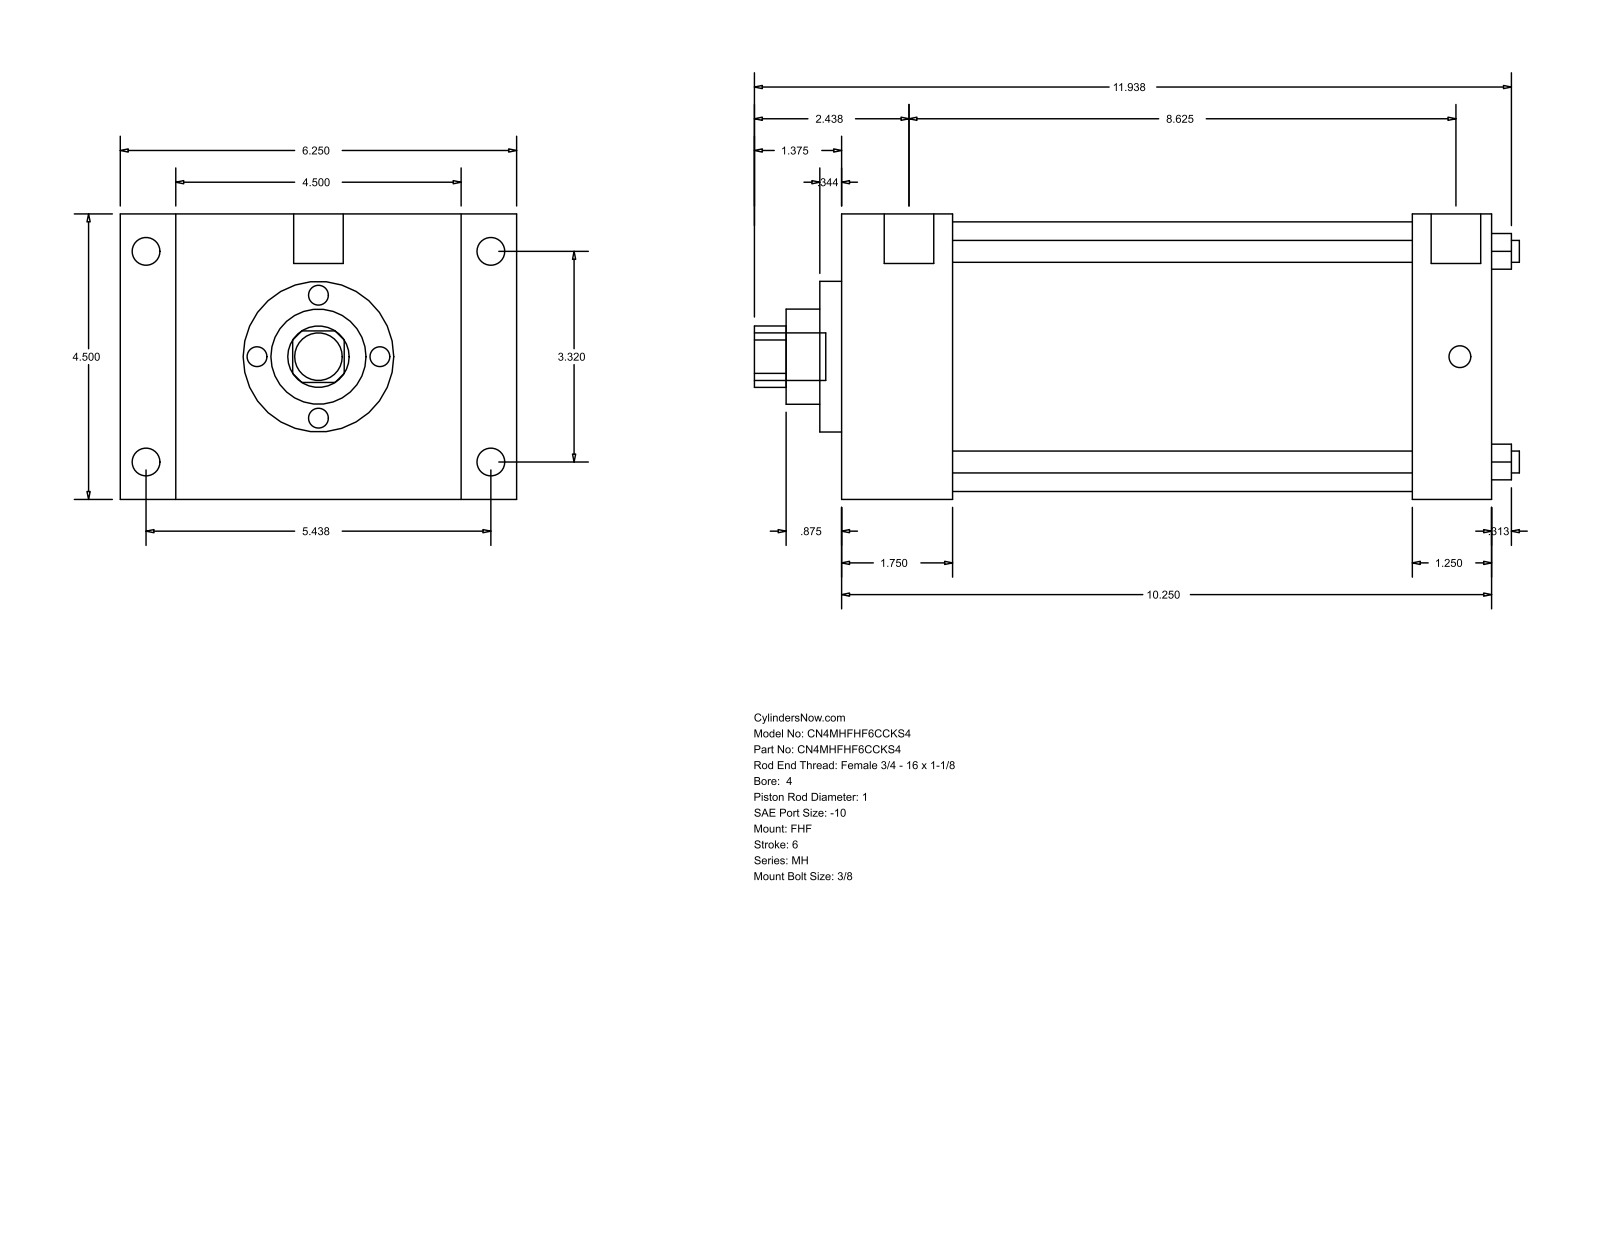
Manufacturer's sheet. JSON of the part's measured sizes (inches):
{"part_name": "MH_FHF__0400_1", "step_written_by": "GSSL Pune (CONFIG_CONTROL_DESIGN)", "units": "inches", "bodies": {"solids": 0, "faces": 90, "planar": 61, "cylindrical": 29, "other": 0}, "overall_size": [12.063, 6.25, 4.5], "round_holes": [[0.345, 4], [1, 1], [1.5, 1], [2.375, 1], [4.25, 1]], "round_bosses_or_shafts": [[0.438, 4], [0.344, 4], [0.781, 2], [0.75, 1]], "partial_cylinders_radius": [[0.484, 1]], "face_to_face_distances": [4.5, 10.25, 1.75, 8.5, 0.875, 5.375, 6.25, 9, 7.25, 1.25], "hole_center_spacings": [2.347, 3.32, 4.695]}
